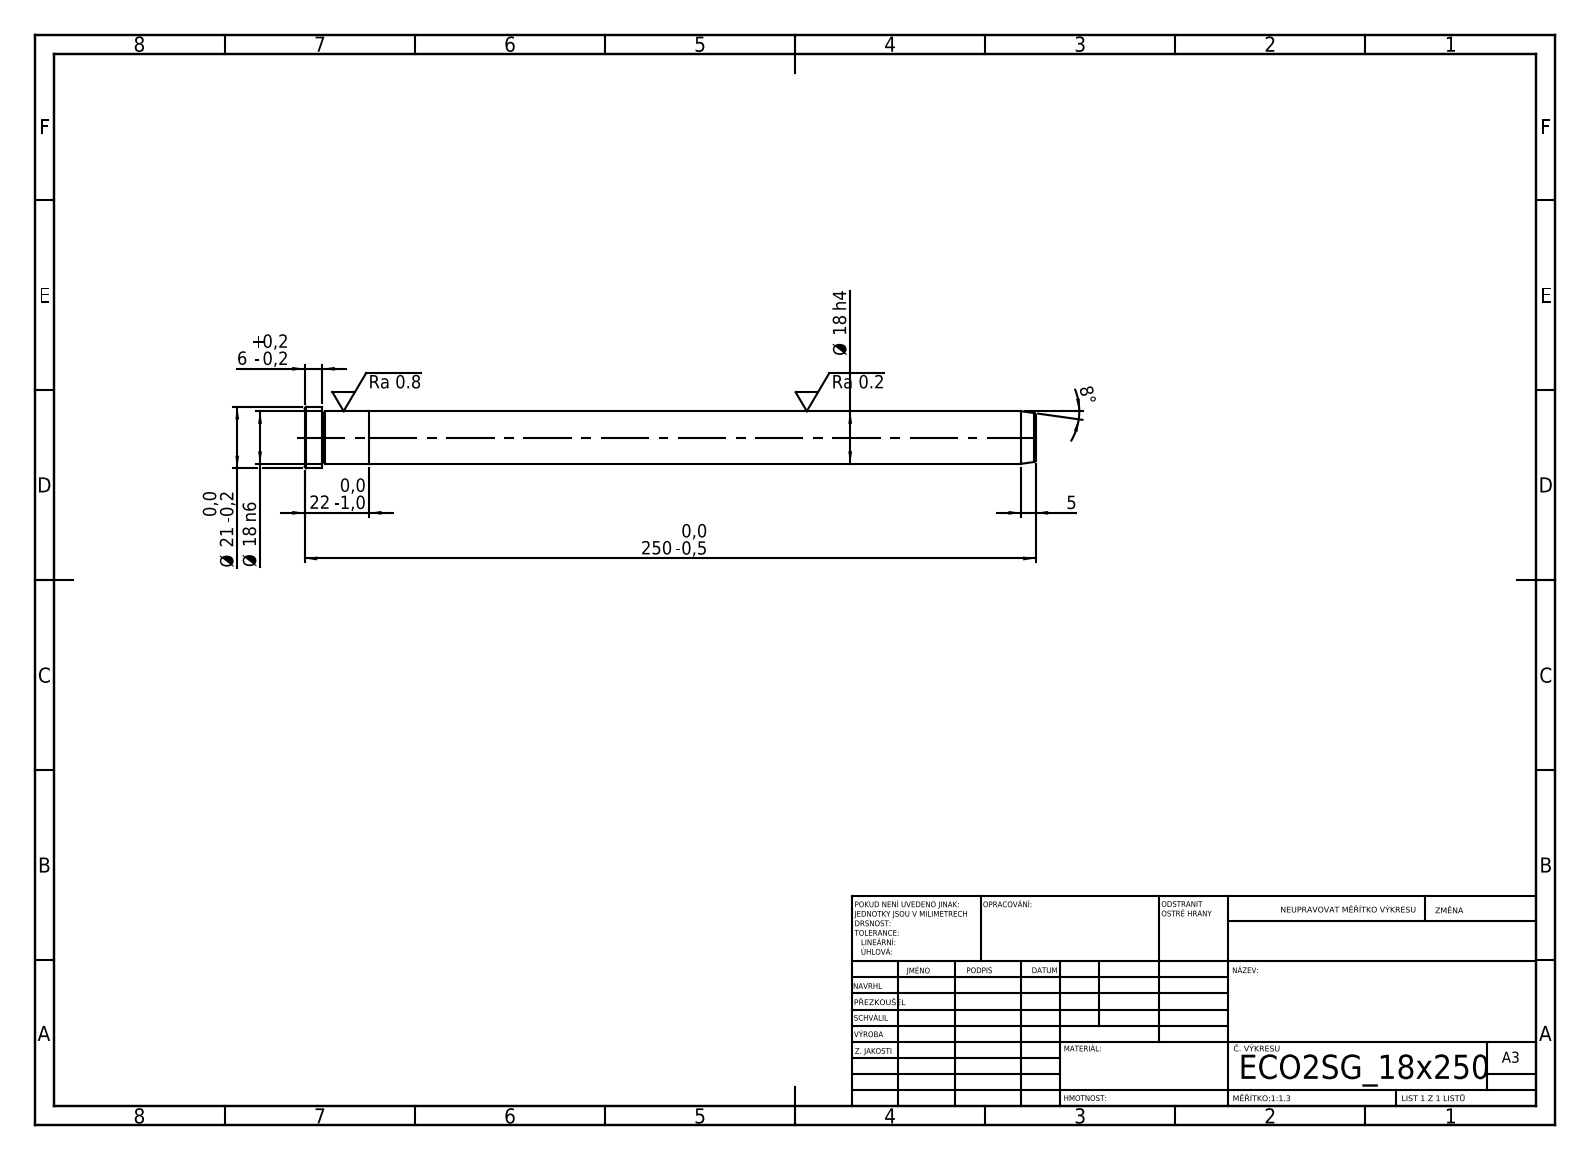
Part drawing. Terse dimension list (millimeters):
written by: SolidWorks 2019 (CONFIG_CONTROL_DESIGN)
unit: mm
bodies: 2 solids, 21 faces (5 planar, 6 cylindrical, 10 other)
size: 250 × 21 × 21
volume: 64 040 mm³; area: 15 350 mm²
bosses: 1× ⌀21, 1× ⌀18
face distances: 22, 228, 250, 244, 16, 6
